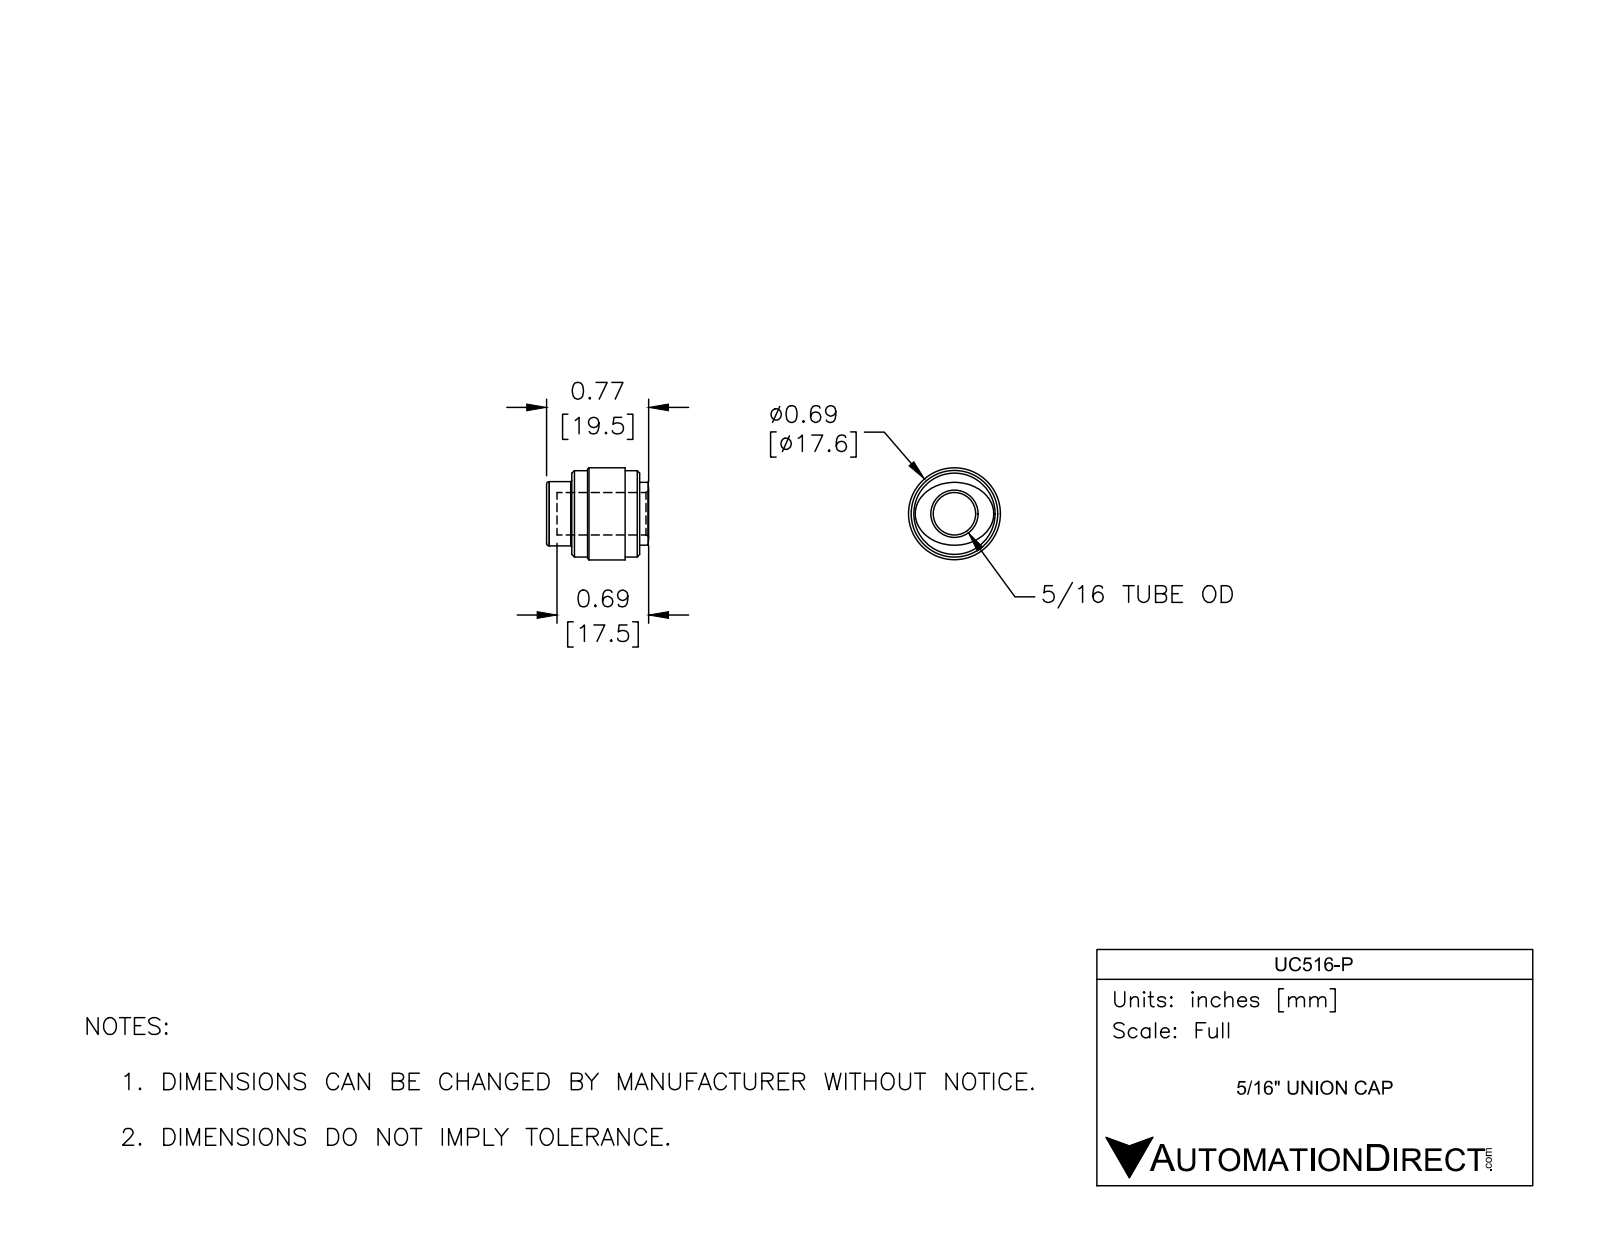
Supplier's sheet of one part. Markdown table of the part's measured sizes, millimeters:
| quantity | value |
| --- | --- |
| part name | UC516-P |
| STEP written by | SolidWorks 2017 (AUTOMOTIVE_DESIGN) |
| units | millimeters |
| bodies | 1 solid, 32 faces (6 planar, 10 cylindrical, 16 other) |
| overall size | 19.5 × 17.6 × 17.6 |
| volume | 2 880 mm³ |
| surface area | 1 826 mm² |
| round holes (diameter × count) | 8.1 × 1 |
| round bosses / shafts (diameter × count) | 17.6 × 1, 16.5 × 1, 12.3 × 1 |
| main face-to-face distances | 2.8, 13, 4.8, 2, 17.8, 15.8, 15, 10.2, 7.8, 5.8 |
